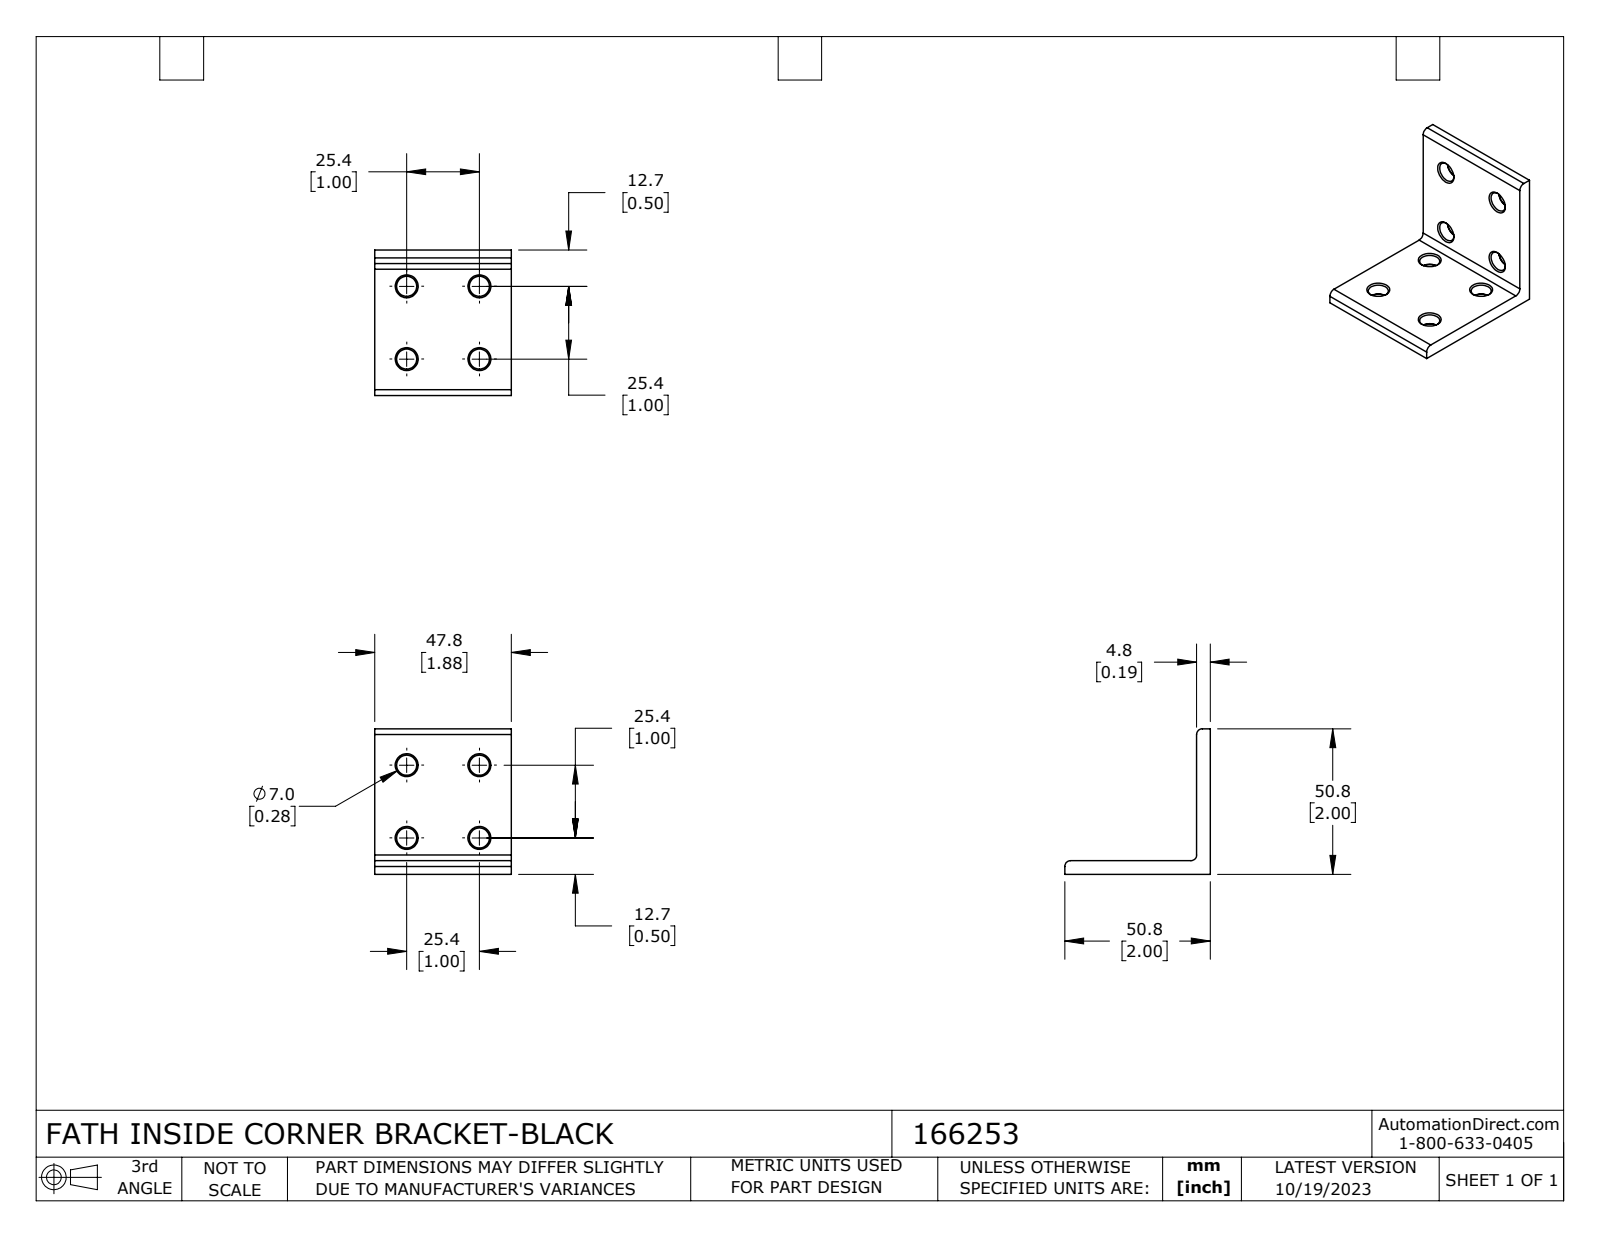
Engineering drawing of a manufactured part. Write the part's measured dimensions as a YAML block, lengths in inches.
part_name: "166253"
step_written_by: "SolidWorks 2023 (CONFIG_CONTROL_DESIGN)"
units: inches
bodies: {solids: 1, faces: 59, planar: 8, cylindrical: 19, other: 32}
overall_size: [2, 2, 1.88]
volume: 1.249
surface_area: 16.47
round_holes:
  - {diameter: 0.276, count: 8}
partial_cylinders:
  - {radius: 0.079, count: 3}
face_to_face_distances: [0.187, 1.88, 2, 1.813]
hole_center_spacings: [1, 1.414]
